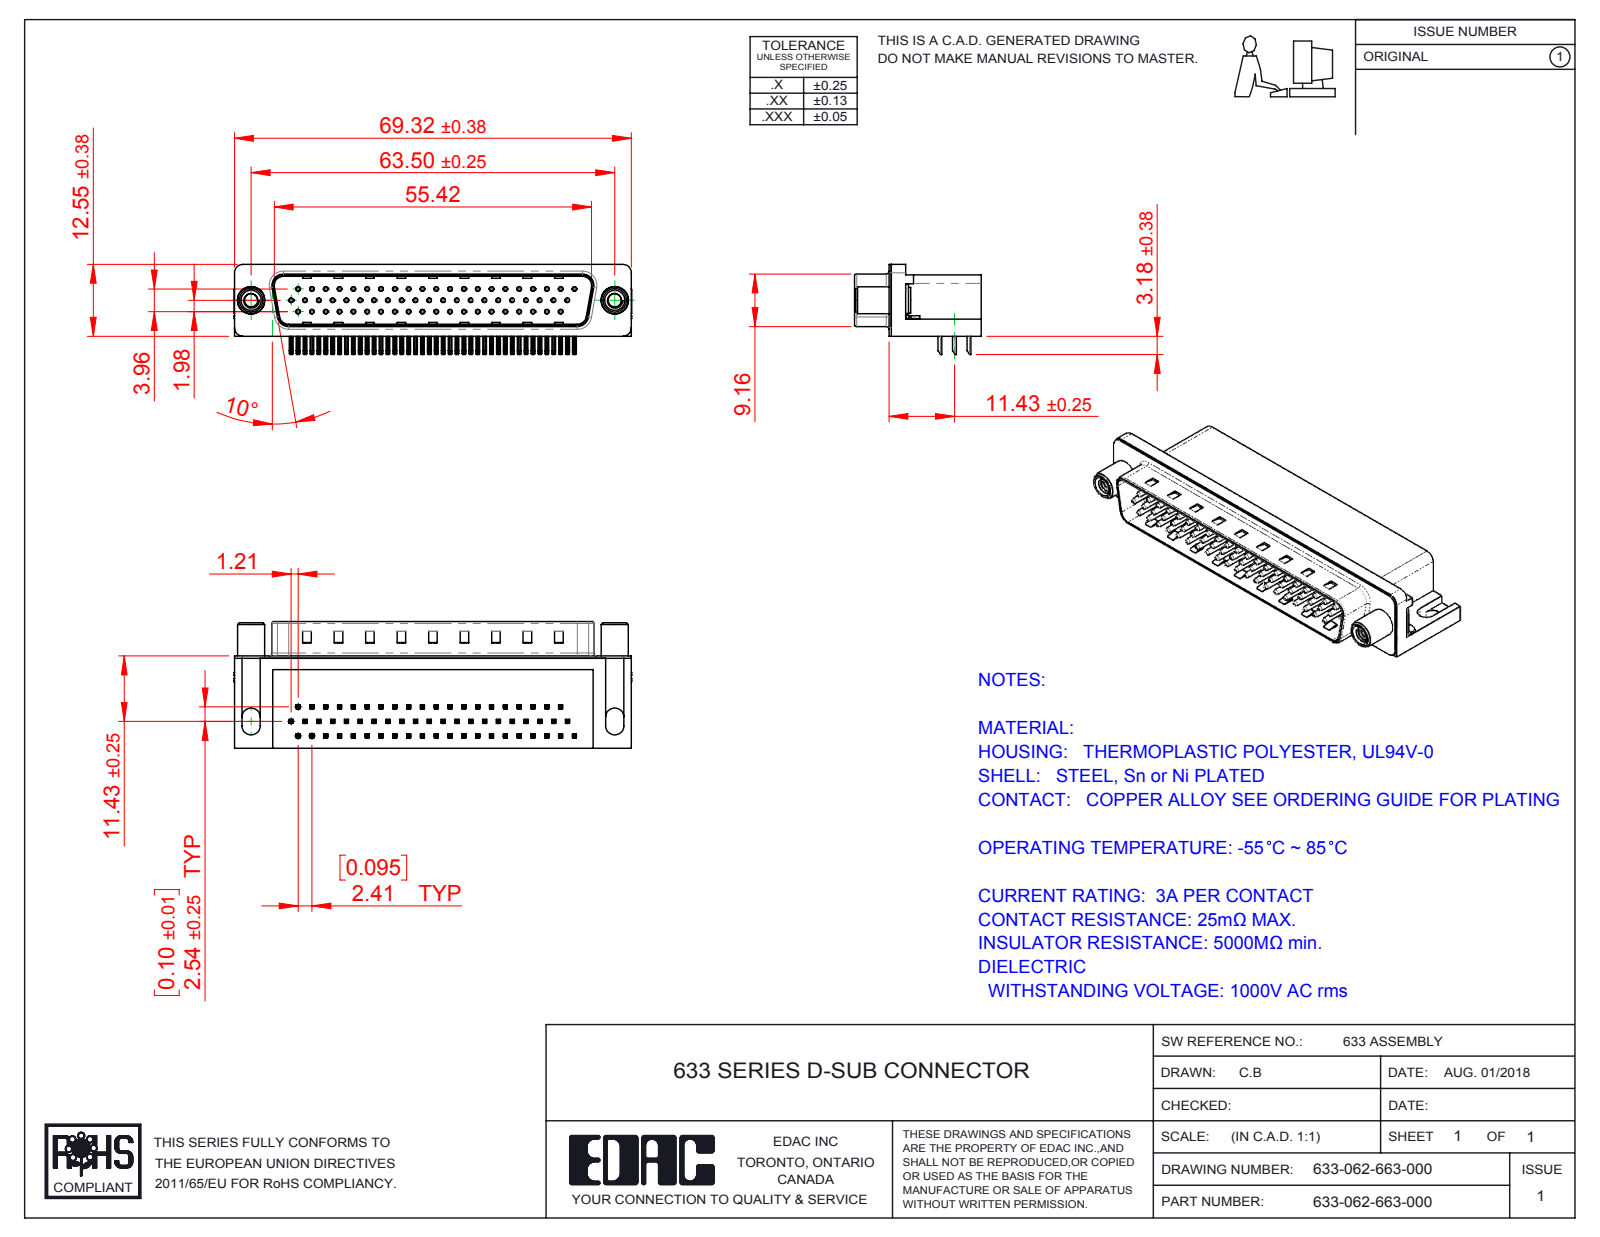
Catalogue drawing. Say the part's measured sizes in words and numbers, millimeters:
The part is named "633 Non Board Mount; 633 Contact Top; 633 Shell_62 Contact; 633 Contact Bottom (+4 more)". Its 3-D file was written by "SolidWorks 2016 (CONFIG_CONTROL_DESIGN)". It is 68 solids with 5066 faces: 3205 planar, 1446 cylindrical and 415 other. Overall it measures 69.4 by 22.1 by 15.73 millimeters. Its volume is 11 098 cubic millimeters and its surface area 13 381 square millimeters. Round holes: 62 of diameter 0.35, 62 of diameter 0.8, 2 of diameter 2.3, 2 of diameter 3.1, 2 of diameter 4, 2 of diameter 4.8, 2 of diameter 5. Round bosses or shafts: 62 of diameter 0.75, 2 of diameter 4.9, 2 of diameter 4.7, 2 of diameter 4.5, 2 of diameter 3.85. Partial cylindrical surfaces (rounded edges, fillets, slot ends): 248 of radius 0.25, 124 of radius 0.12, 16 of radius 1, 9 of radius 0.5, 8 of radius 1.6, 7 of radius 1.5, 4 of radius 0.9, 4 of radius 2. The main face-to-face distances are 0.4, 10.35, 15.7, 8.76, 2.5, 2.9, 2.54, 8.36, 2.1, 8.6. The hole center spacings are 2.41, 4.82, 7.24, 9.65, 14.48, 16.89, 4.83, 7.23.
